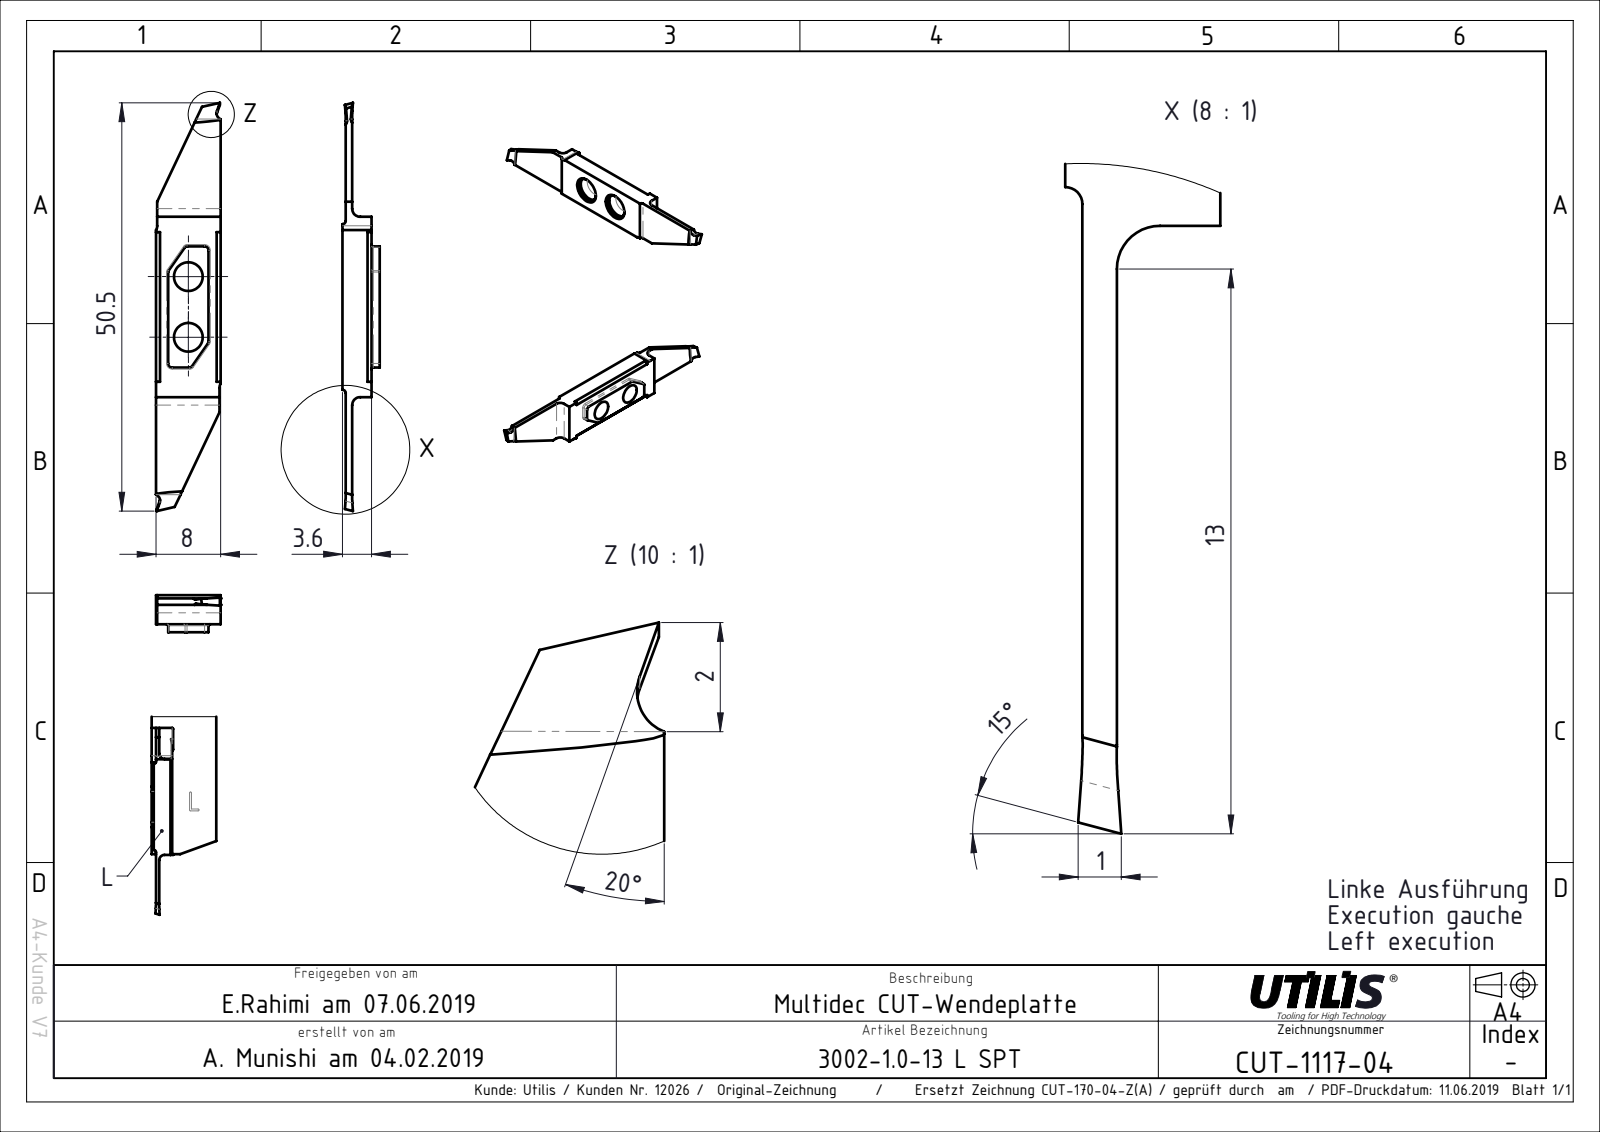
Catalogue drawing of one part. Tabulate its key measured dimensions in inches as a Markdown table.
| quantity | value |
| --- | --- |
| part name | CUT-1117; ASME Y14.5 |
| STEP written by | FormatWorks Professional (AP242_MANAGED_MODEL_BASED_3D_ENGINEERING_MIM_LF) |
| units | inches |
| bodies | 1 solid, 38 faces (28 planar, 10 cylindrical, 0 other) |
| overall size | 1.988 × 0.315 × 0.142 |
| volume | 0.042 in³ |
| surface area | 1.45 in² |
| round holes (diameter × count) | 0.14 × 2 |
| partial cylindrical surfaces (radius × count) | 0.039 × 4, 0.016 × 2 |
| main face-to-face distances | 0.016, 0.142, 0.126, 0.047, 0.031, 0.095, 0.315, 0.878, 0.309, 0.712 |
| hole center spacings | 0.295 |
